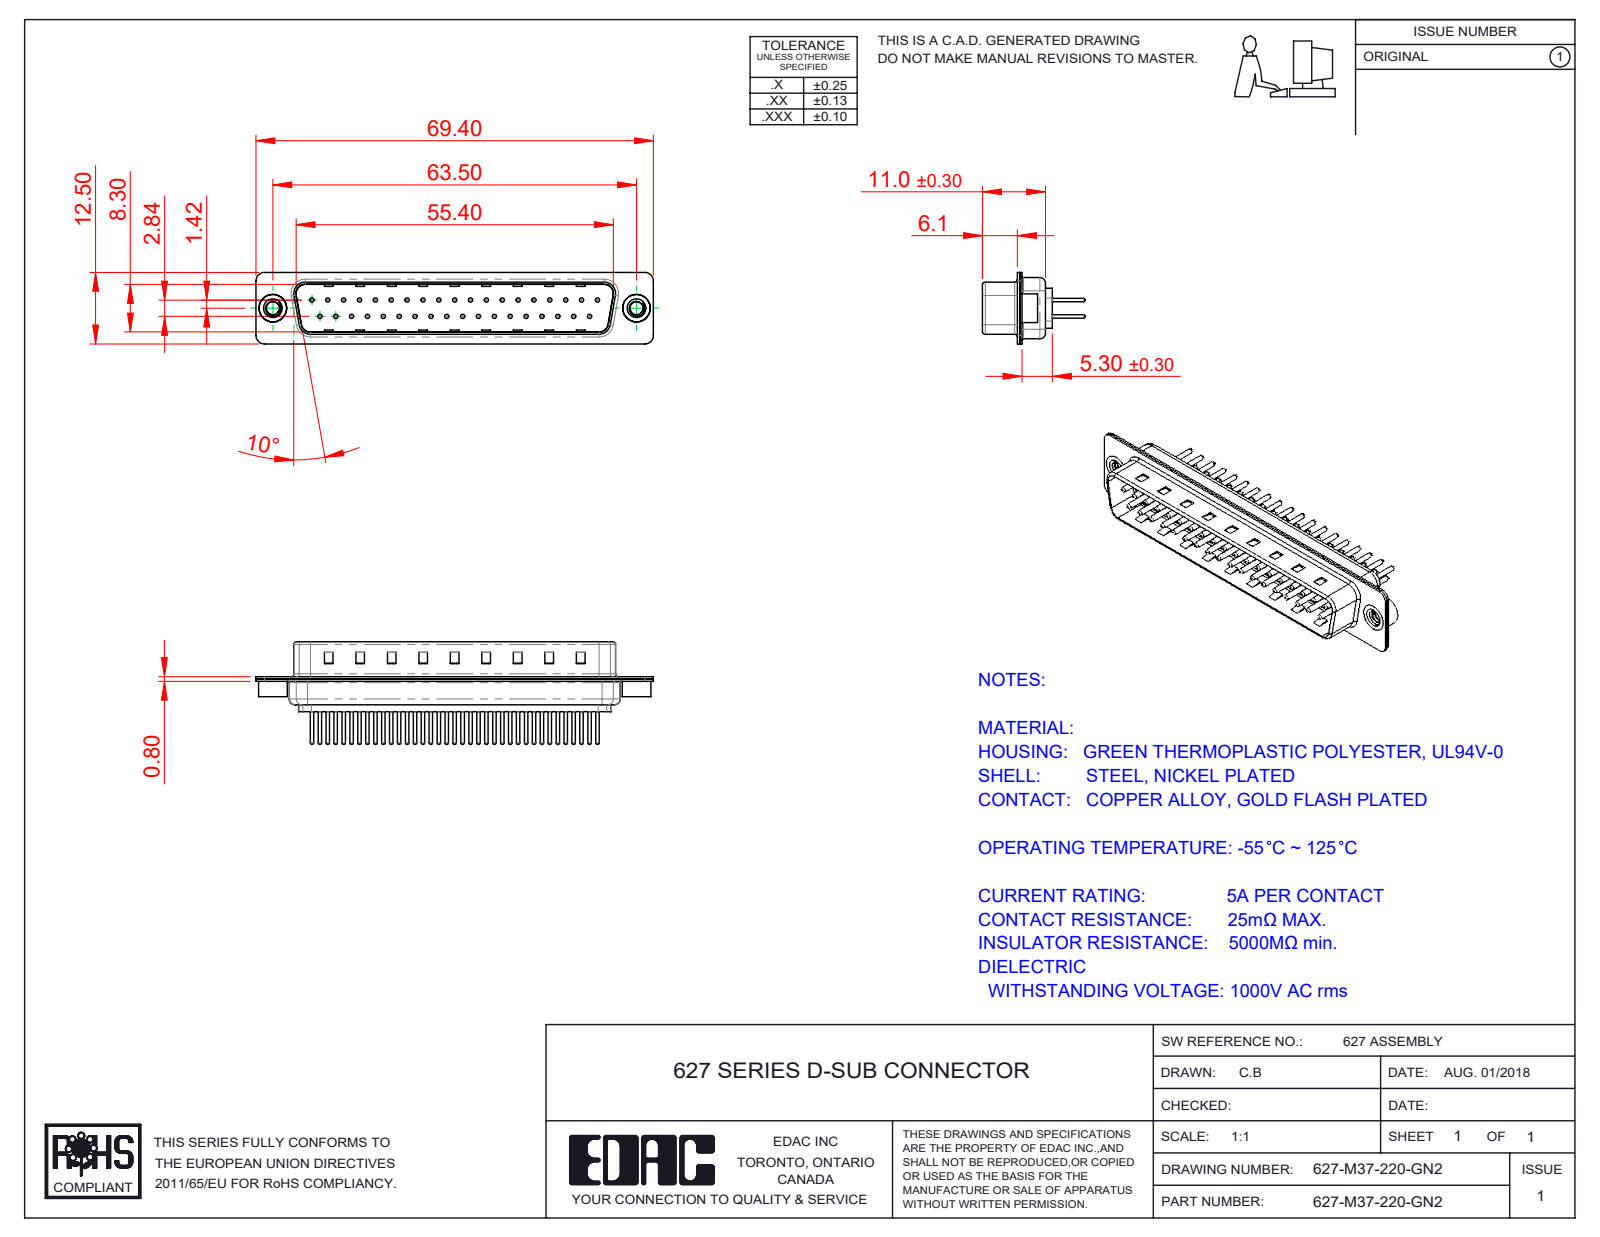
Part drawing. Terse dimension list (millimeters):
name: 627M Shell Front_37 Contacts; 627M Shell Rear_37 Contacts; 627M Contact Row 2_20; 627M Contact Row 1_20 (+3 more)
written by: SolidWorks 2020 (CONFIG_CONTROL_DESIGN)
unit: mm
bodies: 42 solids, 1781 faces (462 planar, 659 cylindrical, 660 other)
size: 69.4 × 17.9 × 12.5
volume: 3 768 mm³; area: 9 269 mm²
holes: 37× ⌀0.75, 37× ⌀1.6, 37× ⌀2, 2× ⌀2.26, 2× ⌀4, 2× ⌀4.8
bosses: 37× ⌀1.5, 37× ⌀0.6, 2× ⌀5, 2× ⌀4.9
rounds: 16× R1.5, 12× R2, 8× R0.5, 8× R1.6, 4× R0.25, 4× R0.6, 4× R0.65, 4× R0.9
face distances: 0.4, 0.8, 9.5, 9.1, 8.7, 9.9, 1.2, 5.7, 0.75, 0.35
hole spacings: 2.77, 5.54, 3.16, 8.31, 11.08, 13.85, 16.62, 19.39
